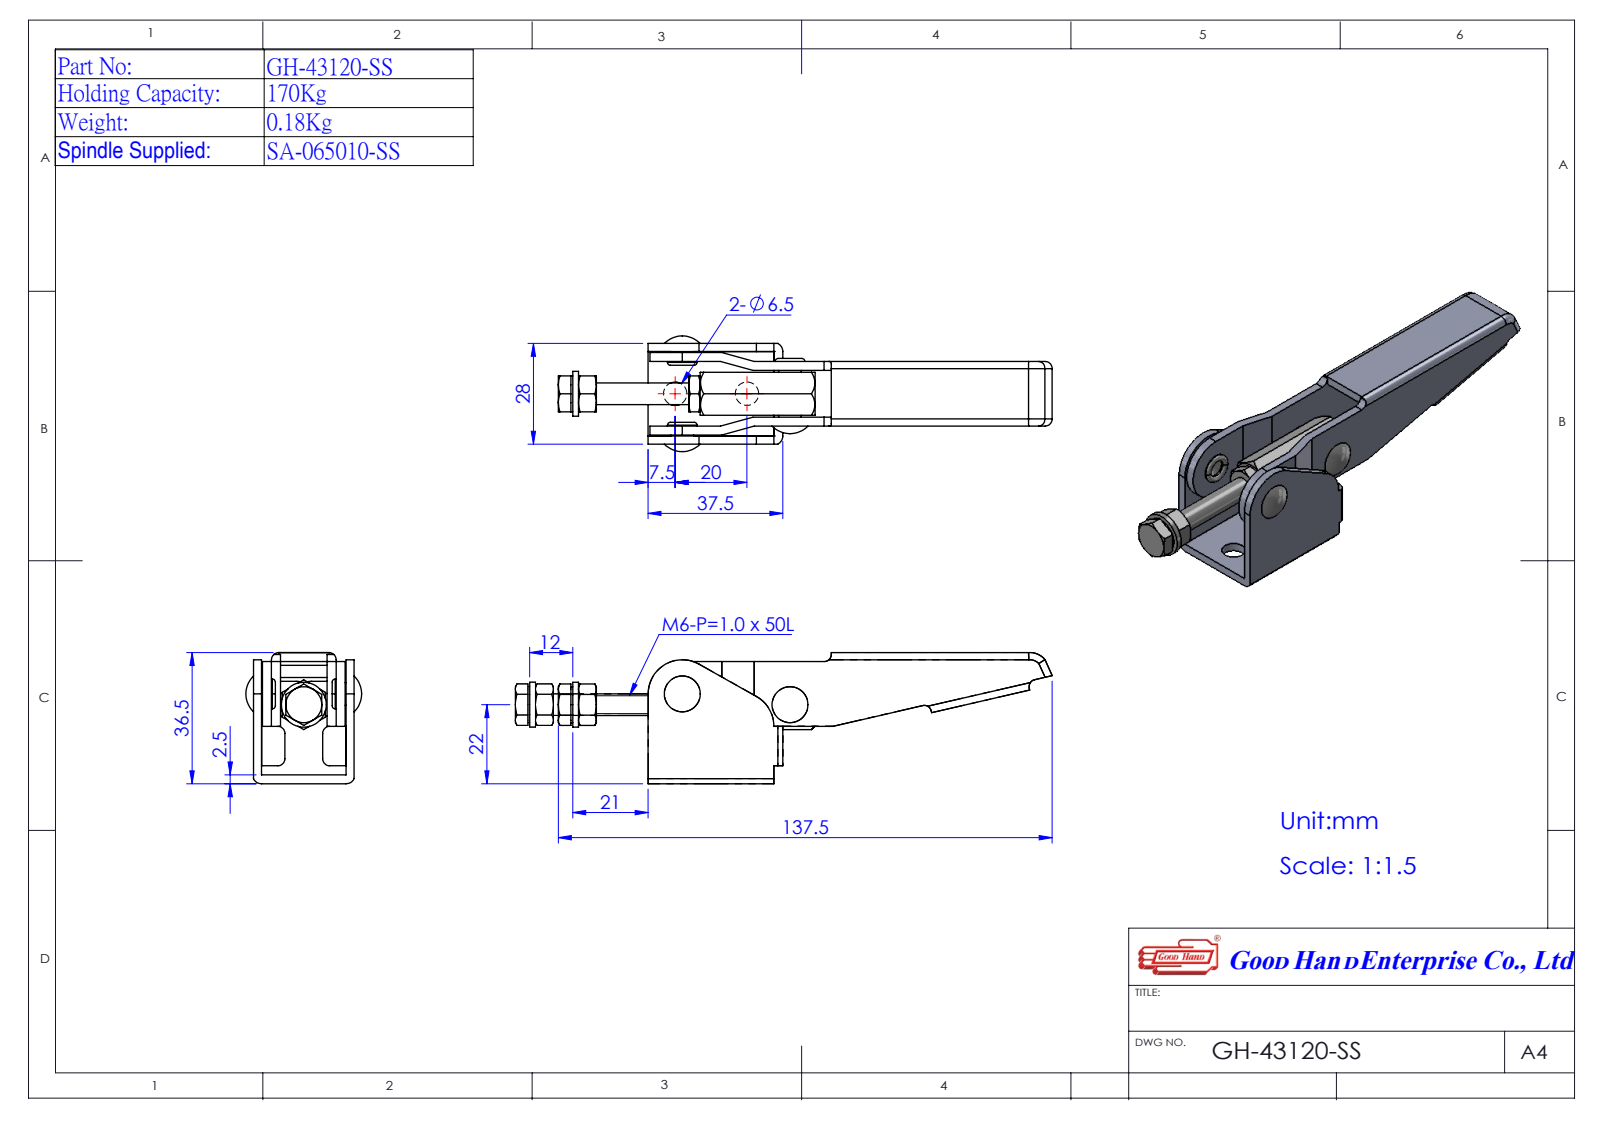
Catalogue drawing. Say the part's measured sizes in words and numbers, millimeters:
The part is named "Group3^GH-43120-SS(簡化); Group1^GH-43120-SS(簡化); Continuous Thread Hexagon Head Bolt_A_JIS-4^GH-43120-SS(簡化); GH-43120-SS(簡化) (+1 more)". Its 3-D file was written by "SolidWorks 2016 (AUTOMOTIVE_DESIGN)". It is 4 solids with 219 faces: 93 planar, 76 cylindrical and 50 other. Overall it measures 136.49 by 36.51 by 32.2 millimeters. Its volume is 24 605 cubic millimeters and its surface area 21 002 square millimeters. Round holes: 3 of diameter 5, 2 of diameter 6.6, 1 of diameter 6, 1 of diameter 7. Round bosses or shafts: 1 of diameter 10, 1 of diameter 8.3, 1 of diameter 6.3. Partial cylindrical surfaces (rounded edges, fillets, slot ends): 17 of radius 2, 4 of radius 2.51, 2 of radius 9.5, 1 of radius 3.51, 1 of radius 5.51, 1 of radius 9. The main face-to-face distances are 2.5, 20.5, 5, 18, 23, 15.5, 2.75, 5.25, 2.25, 18.25. The hole center spacings are 20, 30.15.
